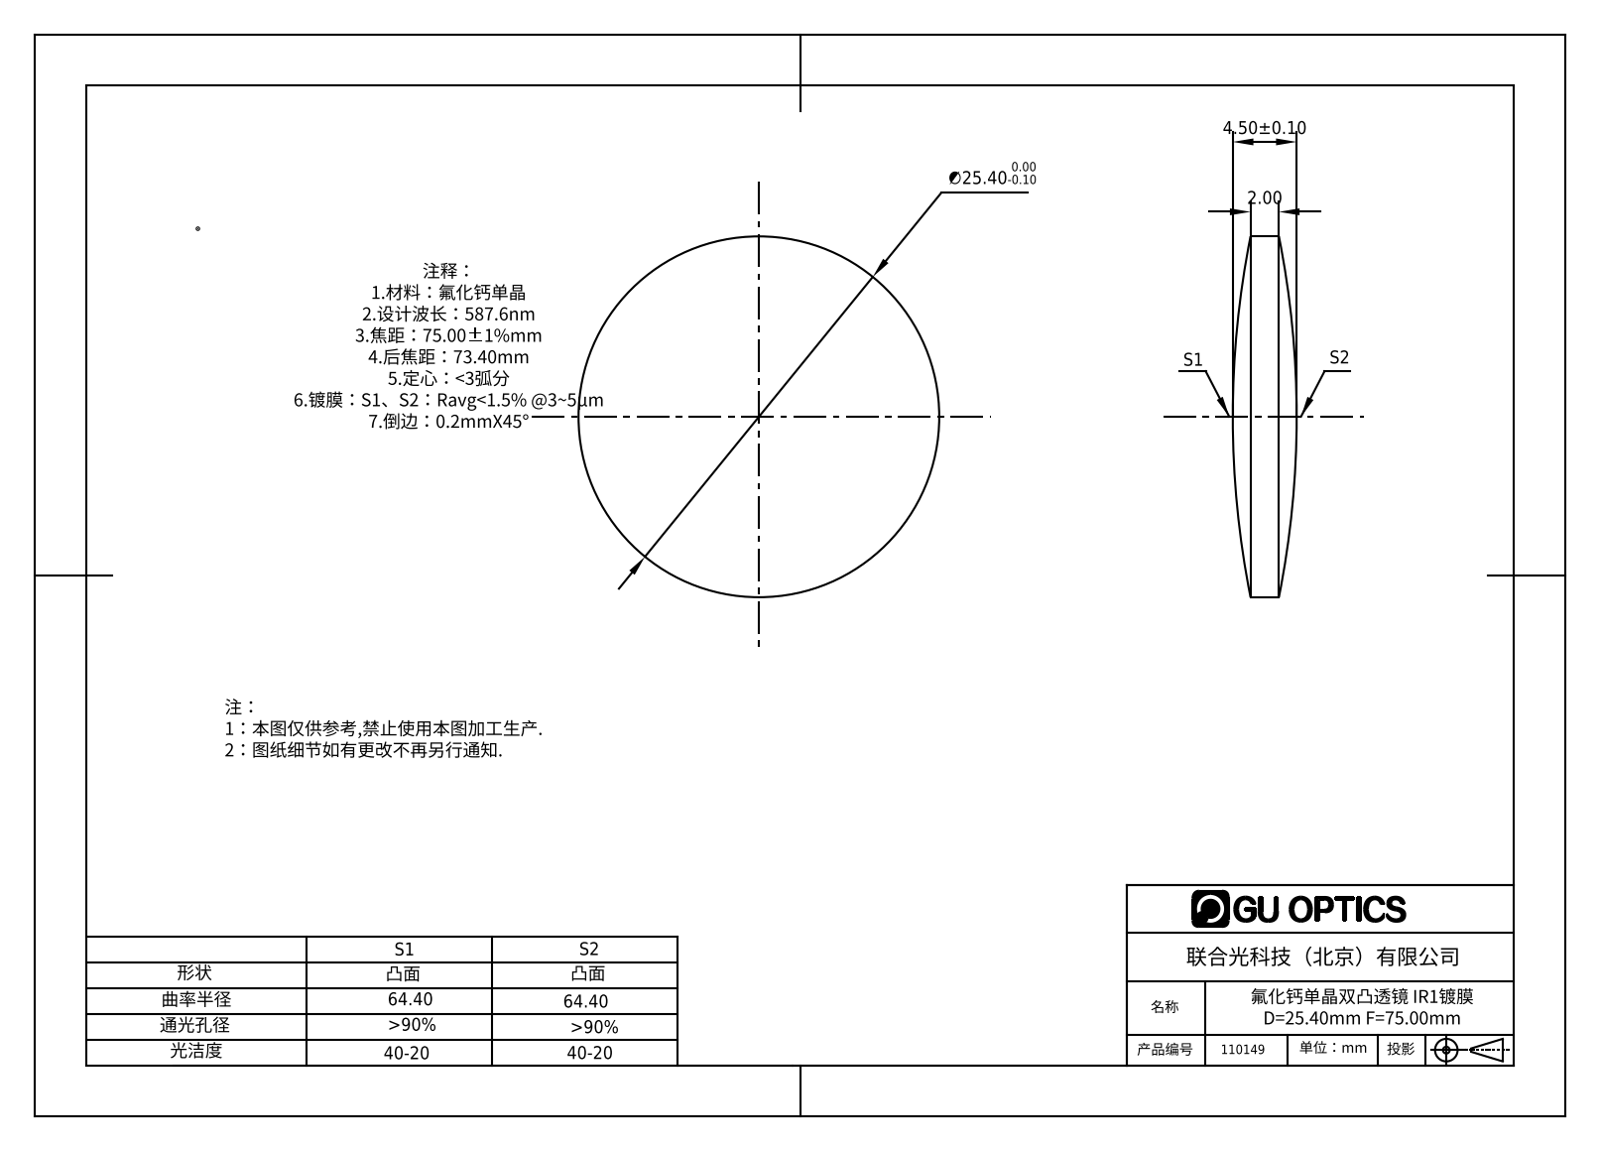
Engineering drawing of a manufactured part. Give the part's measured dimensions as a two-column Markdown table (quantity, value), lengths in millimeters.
| quantity | value |
| --- | --- |
| part name | 110141 |
| STEP written by | SolidWorks 2016 (CONFIG_CONTROL_DESIGN) |
| units | millimeters |
| bodies | 1 solid, 6 faces (0 planar, 2 cylindrical, 4 other) |
| overall size | 25.4 × 25.4 × 4.5 |
| volume | 1 649 mm³ |
| surface area | 1 183 mm² |
| round bosses / shafts (diameter × count) | 25.4 × 1 |
